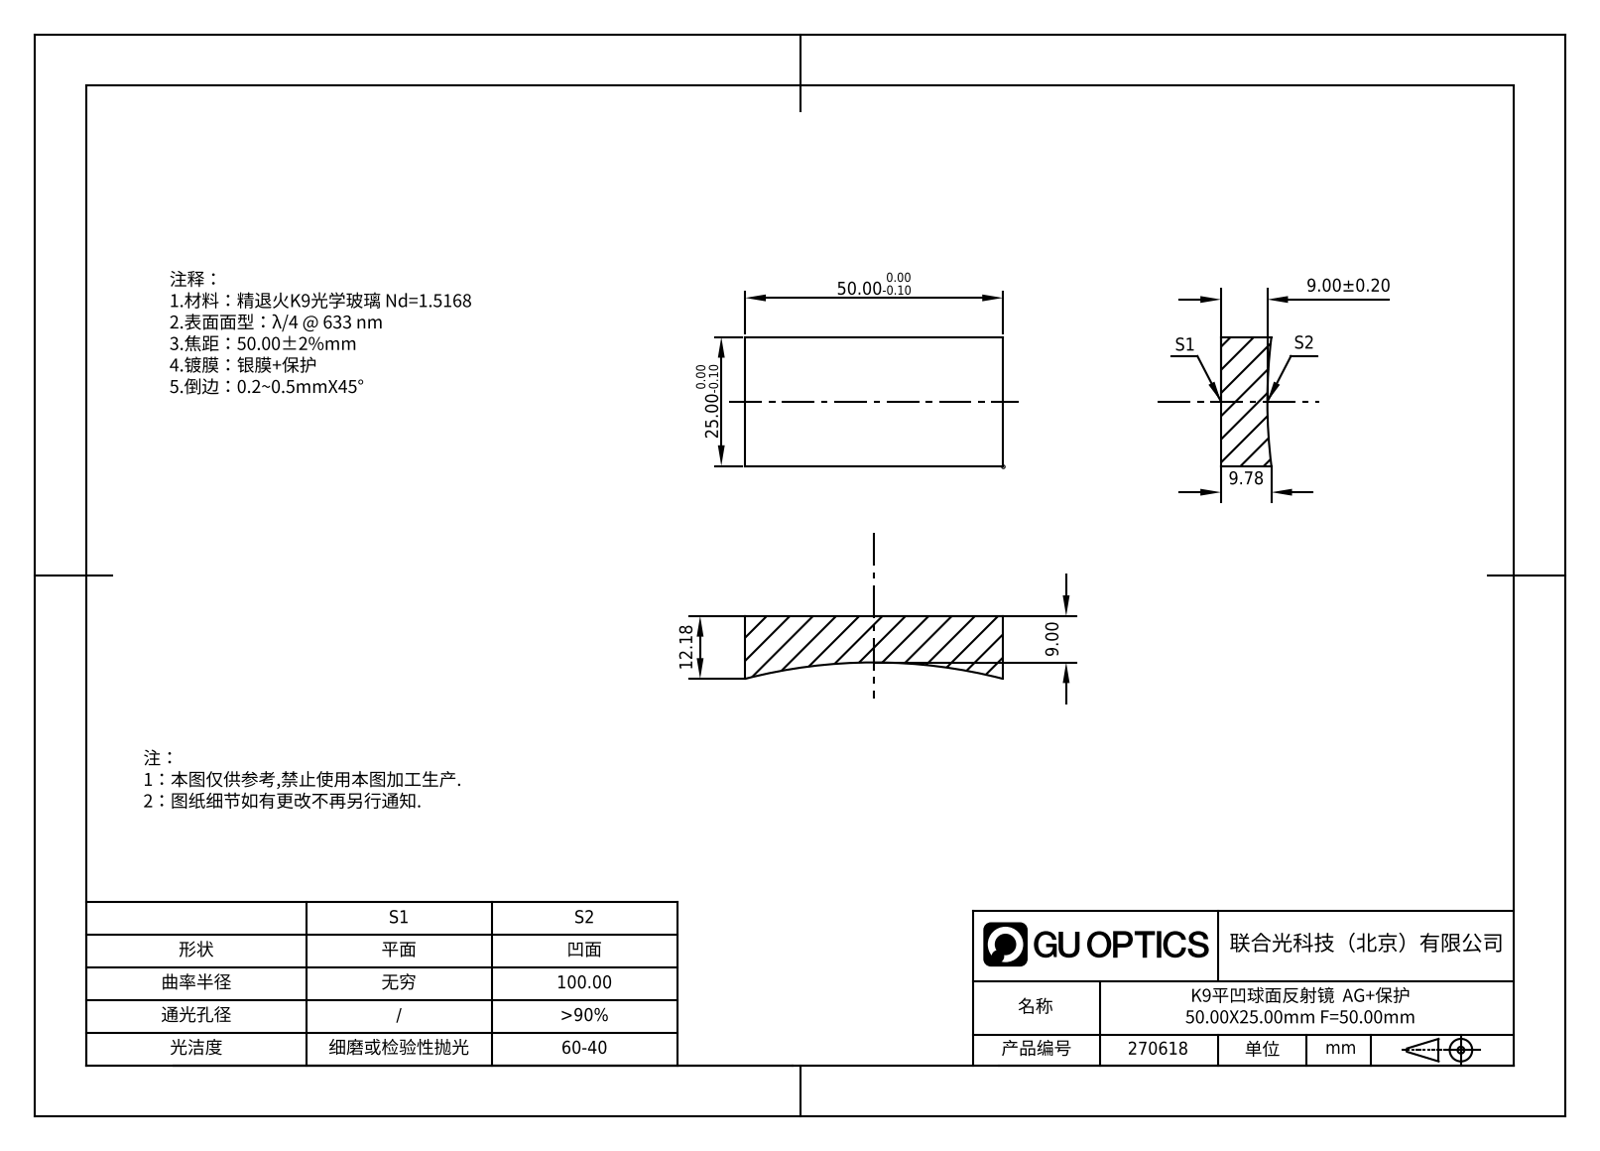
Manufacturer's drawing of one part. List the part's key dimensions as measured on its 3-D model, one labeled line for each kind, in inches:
Part name (STEP PRODUCT): GM13-50x25-050
STEP written by: SolidWorks 2022 (AUTOMOTIVE_DESIGN)
Units: inches
Bodies: 1 solid, 7 faces (5 planar, 0 cylindrical, 2 other)
Overall size (bounding box): 1.969 × 0.984 × 0.511
Volume: 0.787 in³ · Surface area: 6.546 in²
Main face-to-face distances: 0.984, 1.969
